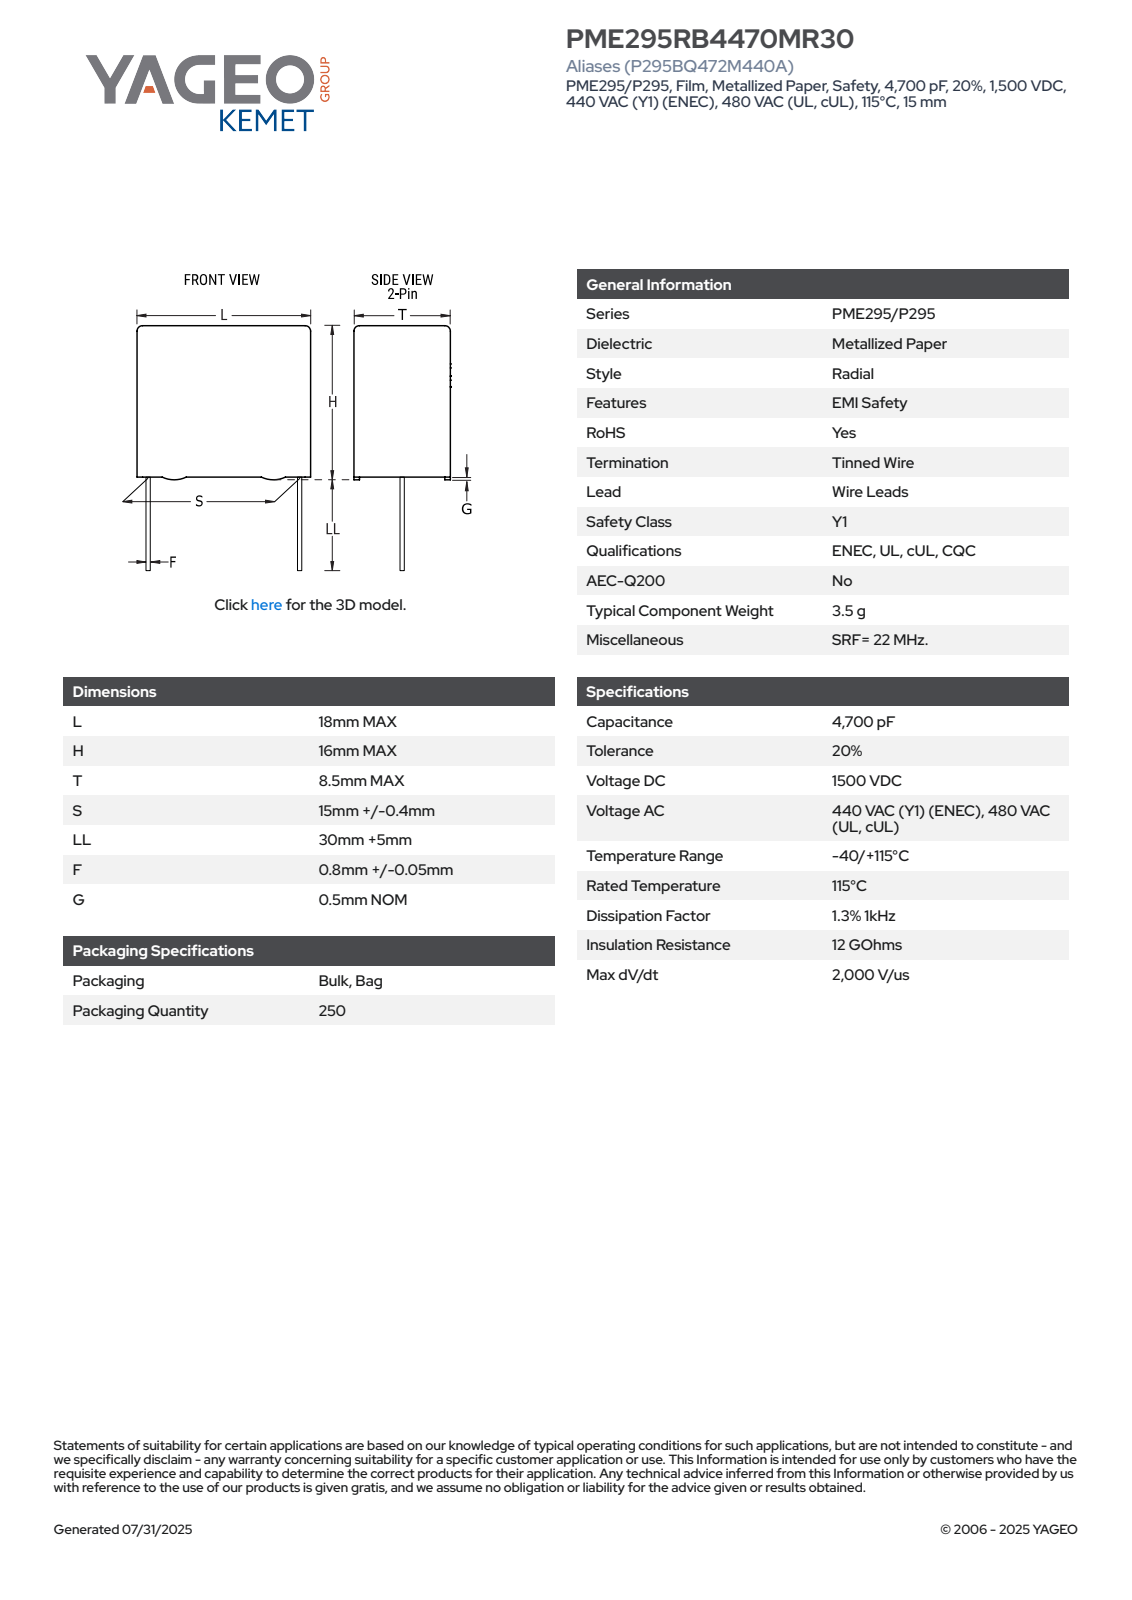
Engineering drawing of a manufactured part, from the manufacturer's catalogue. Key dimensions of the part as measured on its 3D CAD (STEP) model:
Part name (STEP PRODUCT): CFR_RBG_18X16X8.5_L18H16T8.5S15LL35F0.85G0.5
STEP written by: SolidWorks 2014 (AUTOMOTIVE_DESIGN)
Units: millimetres
Bodies: 4 solids, 89 faces (81 planar, 8 cylindrical, 0 other)
Overall size (bounding box): 51 × 18 × 8.51
Volume: 2 412 mm³ · Surface area: 1 354 mm²
Round bosses / shafts (diameter × count): ⌀0.85 ×2
Partial cylindrical surfaces — rounded edges, fillets, slot ends (radius × count): R0.5 ×4
Main face-to-face distances: 8.5, 18, 15.5, 8.51, 0.48, 8.02, 0.5, 16, 8.03, 0.49
